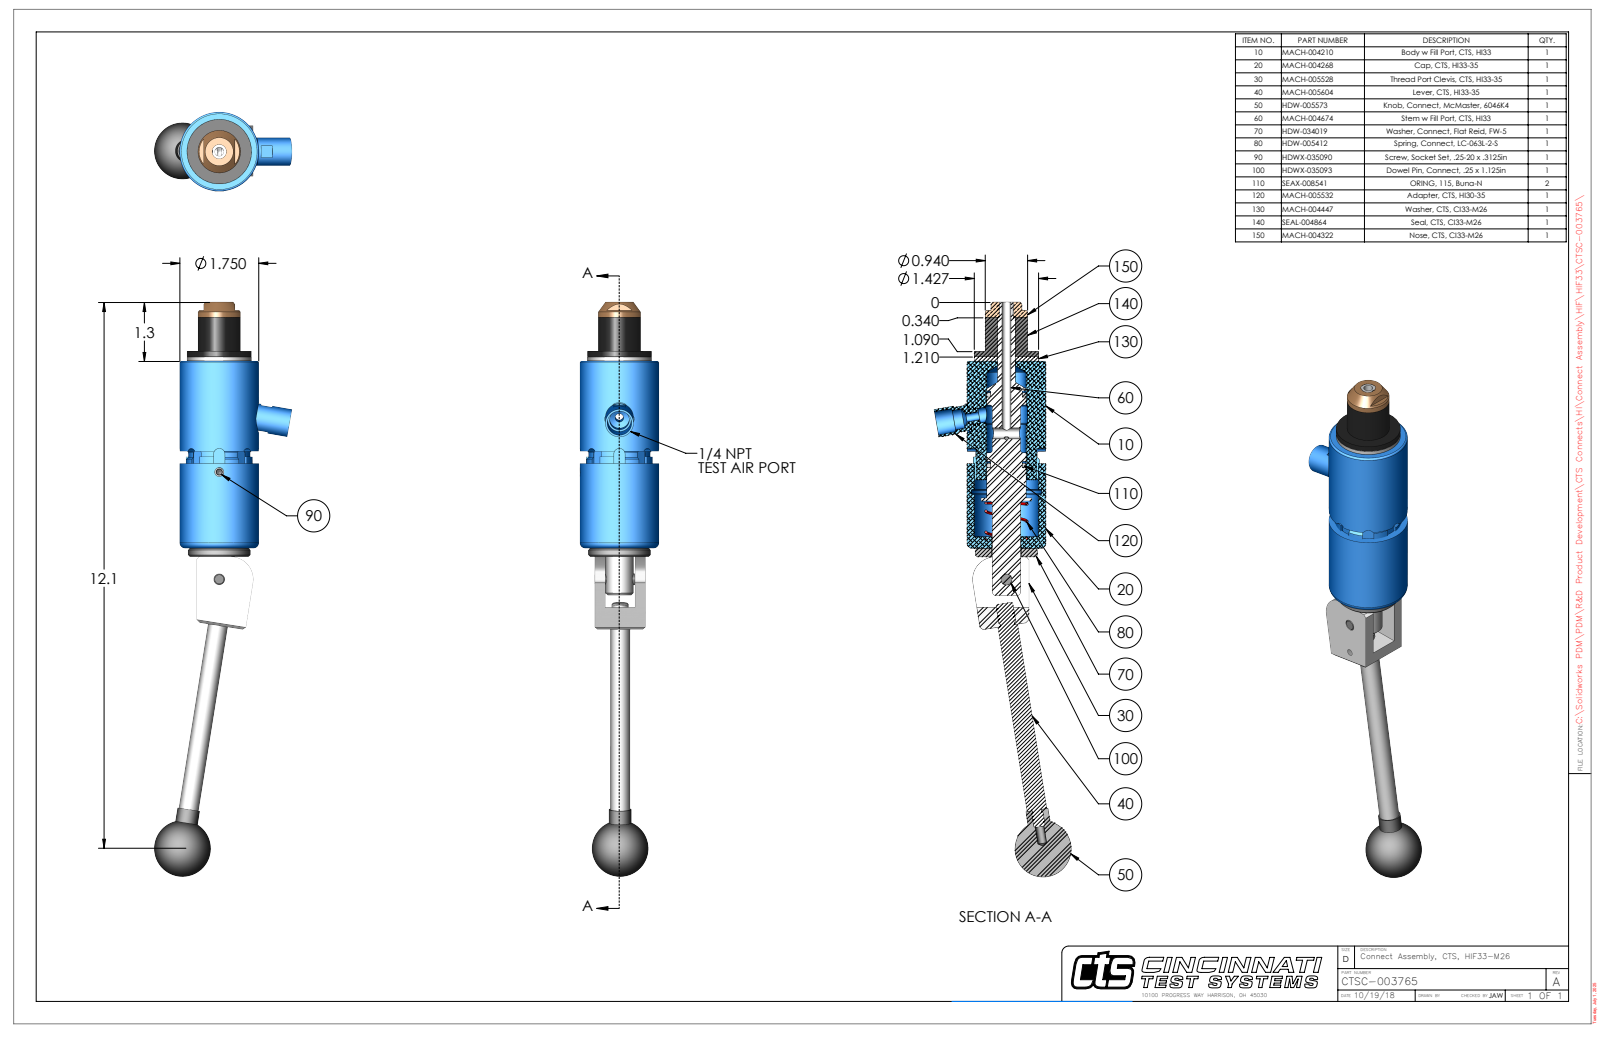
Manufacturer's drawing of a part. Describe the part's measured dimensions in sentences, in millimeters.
The part is named "CTSC-003765". Its 3-D file was written by "SolidWorks 2023 (AUTOMOTIVE_DESIGN)". It is 9 solids with 321 faces: 114 planar, 139 cylindrical and 68 other. Overall it measures 323.3 by 77.3 by 44.5 millimeters. Its volume is 231 200 cubic millimeters and its surface area 50 700 square millimeters. Round holes: 2 of diameter 5.1, 2 of diameter 8, 1 of diameter 3.8, 1 of diameter 4.7, 1 of diameter 5.2, 1 of diameter 6.3, 1 of diameter 6.4, 1 of diameter 6.4, 1 of diameter 9.9, 1 of diameter 10.1, 1 of diameter 10.1, 1 of diameter 11.1. Round bosses or shafts: 2 of diameter 9.5, 2 of diameter 7.9, 2 of diameter 6.4, 1 of diameter 44.5, 1 of diameter 36.2, 1 of diameter 35.1, 1 of diameter 23.9, 1 of diameter 15.9. Partial cylindrical surfaces (rounded edges, fillets, slot ends): 4 of radius 3.2, 2 of radius 0.7, 1 of radius 3.6, 1 of radius 4.2, 1 of radius 4.2, 1 of radius 8.4, 1 of radius 12.7, 1 of radius 17.7. The main face-to-face distances are 2.5, 107.8, 105.3, 28.4, 112.6, 110.1, 4.8, 22.6, 5.9, 5.9. The hole center spacings are 18.8, 60.4, 79.1.
